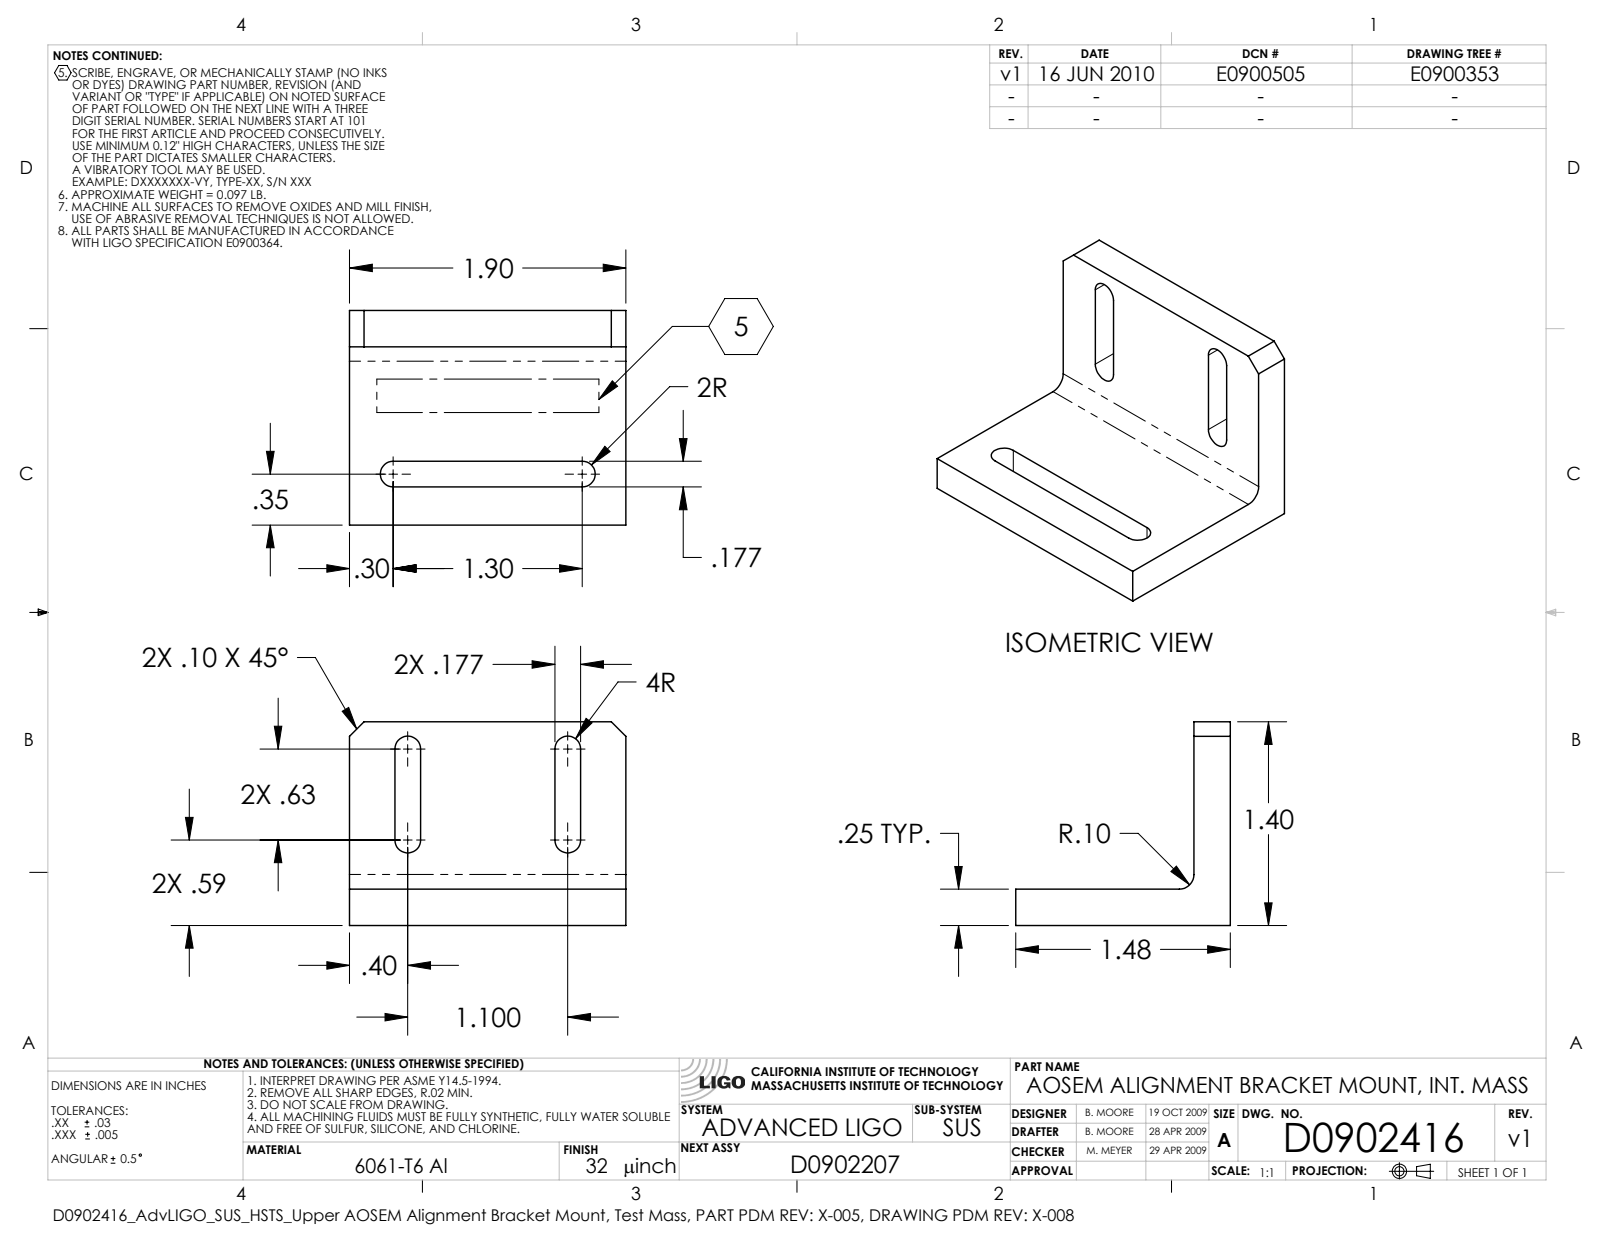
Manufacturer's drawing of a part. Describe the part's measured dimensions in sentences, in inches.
The part is named "D0902416-v1_aLIGO_SUS_HSTS_Upper AOSEM Alignment Bracket Mount, Test Mass". Its 3-D file was written by "SolidWorks 2009 (CONFIG_CONTROL_DESIGN)". It is 1 solid with 26 faces: 16 planar, 10 cylindrical and 0 other. Overall it measures 1.9 by 1.475 by 1.4 inches. Its volume is 1.117 cubic inches and its surface area 12.75 square inches. Partial cylindrical surfaces (rounded edges, fillets, slot ends): 6 of radius 0.089, 1 of radius 0.1. The main face-to-face distances are 0.25, 1.9, 1.475, 1.225, 1.4, 1.15, 1.037, 1.213, 0.787, 0.963.
